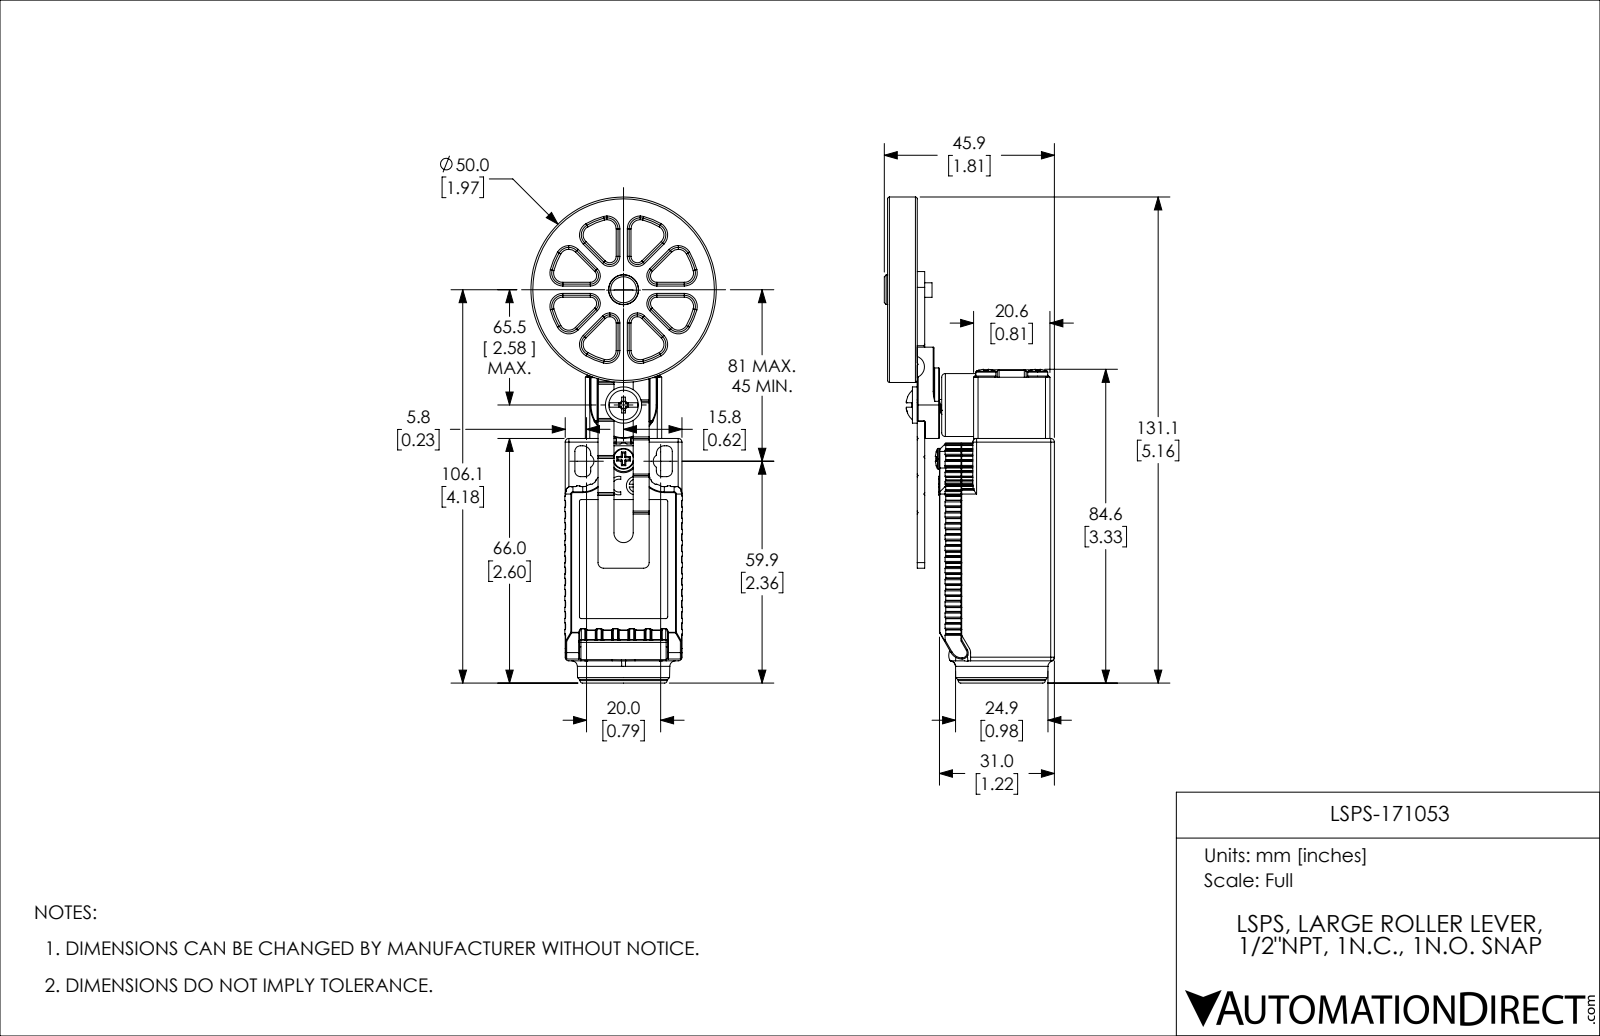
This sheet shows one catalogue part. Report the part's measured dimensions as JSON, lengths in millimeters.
{"part_name": "171-LSPS-Large Roller Lever (STEP format)", "step_written_by": "SolidWorks 2015 (CONFIG_CONTROL_DESIGN)", "units": "millimeters", "bodies": {"solids": 14, "faces": 2923, "planar": 1200, "cylindrical": 1204, "other": 519}, "overall_size": [131.1, 50, 45.9], "volume_mm3": 44357, "surface_area_mm2": 39258, "round_holes": [[2.3, 5], [2.8, 4], [3.2, 4], [5.5, 4], [4, 2], [2.9, 1], [4.1, 1], [5, 1], [6.1, 1], [7.2, 1], [8, 1], [9.8, 1]], "round_bosses_or_shafts": [[1.7, 5], [5.4, 4], [2.5, 4], [50, 1], [23.5, 1], [17.7, 1], [17, 1], [10, 1]], "partial_cylinders_radius": [[0.5, 173], [0.2, 130], [0.1, 92], [0.3, 37], [0.34, 32], [1, 23], [3, 19], [2, 18]], "face_to_face_distances": [2, 8, 4, 6, 10, 29.25, 2.25, 14, 31.5, 1], "hole_center_spacings": [9.9, 14, 7.76, 8.22, 11.96, 16.4, 19.8, 20]}
